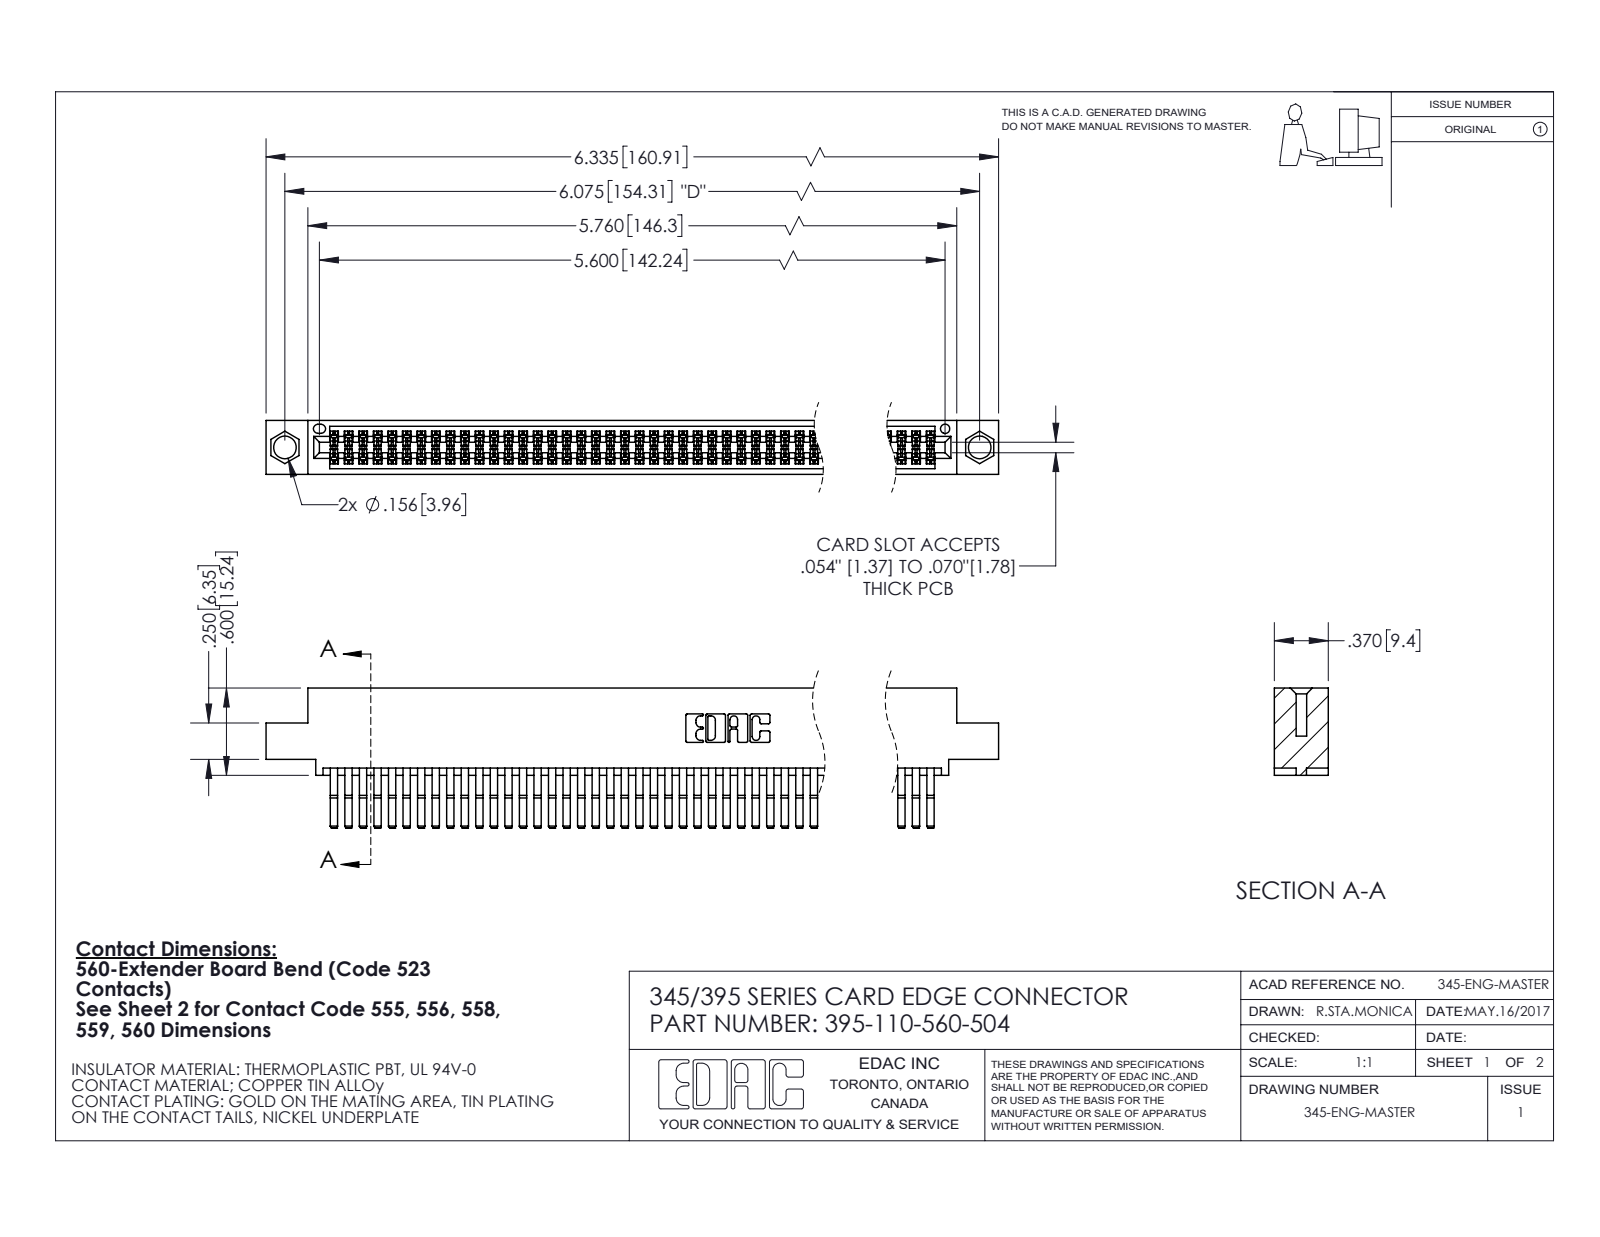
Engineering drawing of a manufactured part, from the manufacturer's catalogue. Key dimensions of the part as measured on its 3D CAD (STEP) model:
Part name (STEP PRODUCT): 345-292-001_560 Tail; 345 Part_0.110 Offset - 0.156 Dia-TI; 395-110-560-504
STEP written by: SolidWorks 2020 (CONFIG_CONTROL_DESIGN)
Units: inches
Bodies: 111 solids, 5864 faces (3728 planar, 2136 cylindrical, 0 other)
Overall size (bounding box): 6.335 × 0.962 × 0.37
Volume: 0.994 in³ · Surface area: 40.51 in²
Round holes (diameter × count): ⌀0.156 ×2, ⌀0.064 ×1
Partial cylindrical surfaces — rounded edges, fillets, slot ends (radius × count): R0.006 ×220, R0.01 ×22, R0.007 ×6, R0.031 ×6, R0.026 ×3, R0.01 ×2, R0.014 ×2, R0.019 ×2
Main face-to-face distances: 0.025, 0.298, 0.072, 0.37, 0.2, 0.098, 0.272, 0.225, 0.175, 0.149
Hole centre spacings: 0.27, 5.839, 6.075
